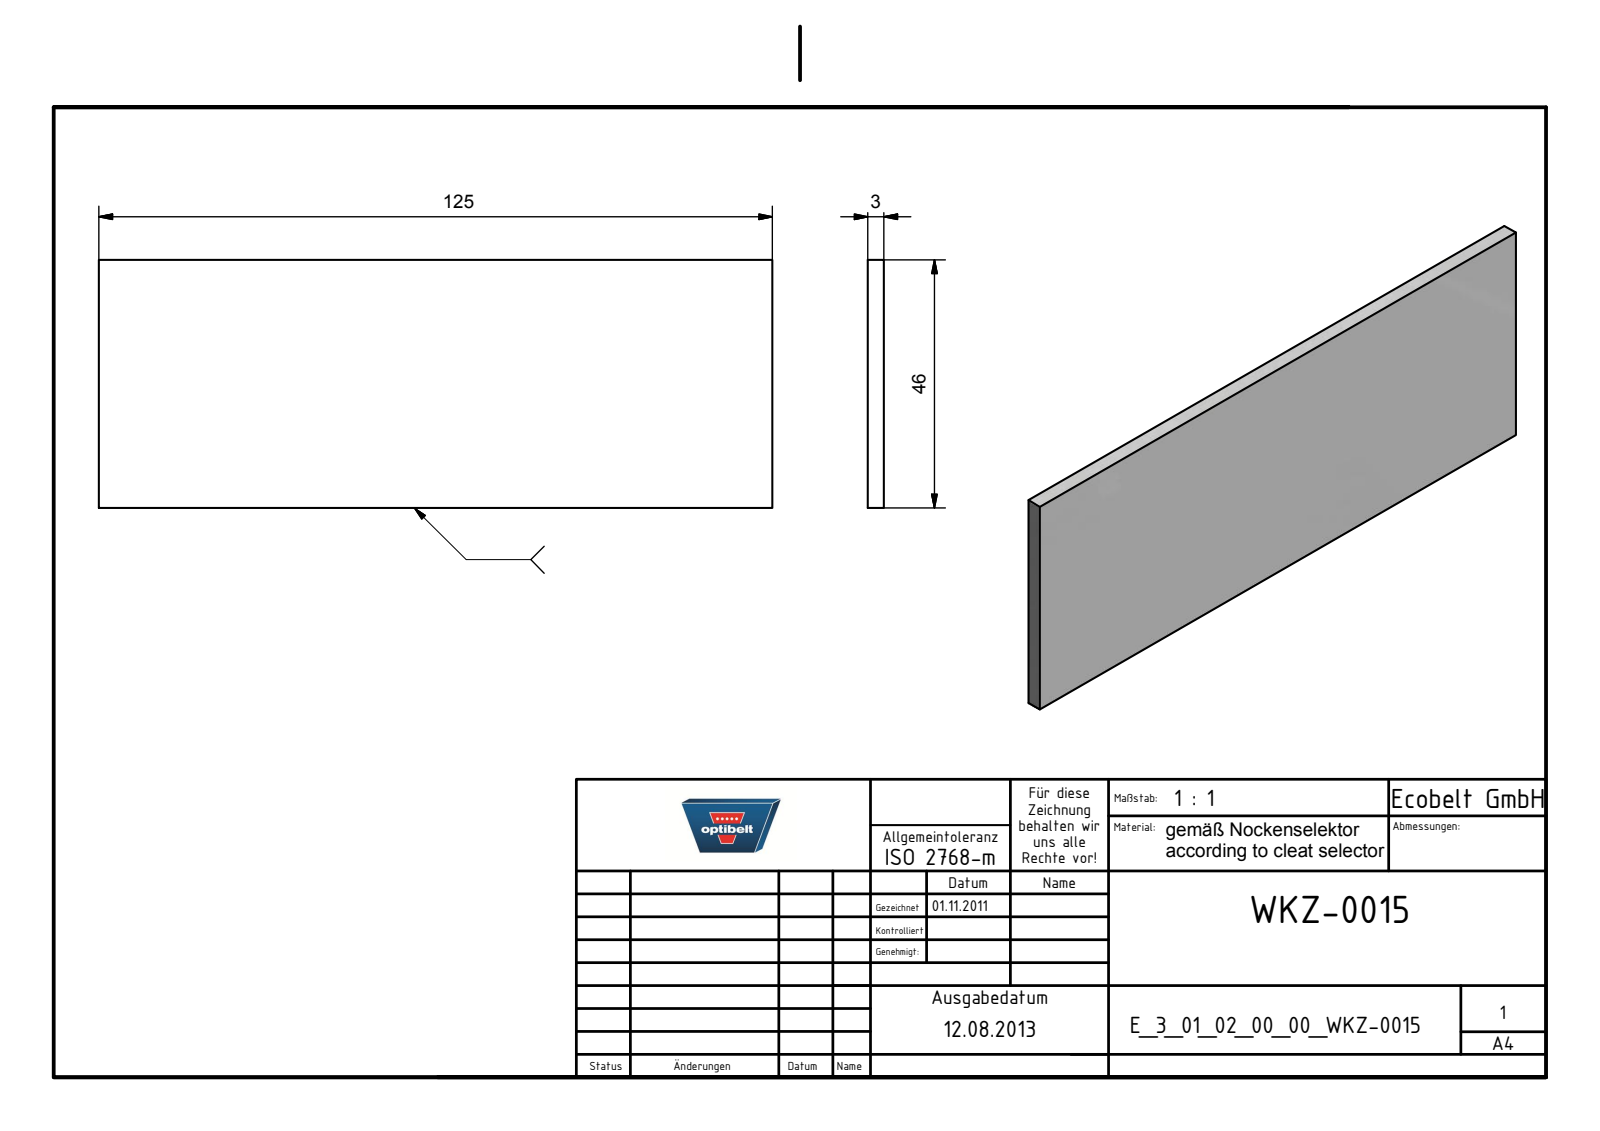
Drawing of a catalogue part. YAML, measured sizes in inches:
part_name: "E_3_01_02_00_00_WKZ-0015"
step_written_by: "Autodesk Inventor 2021 (AUTOMOTIVE_DESIGN)"
units: inches
bodies: {solids: 1, faces: 6, planar: 6, cylindrical: 0, other: 0}
overall_size: [4.921, 1.811, 0.118]
volume: 1.053
surface_area: 19.42
face_to_face_distances: [0.118, 1.811, 4.921]
